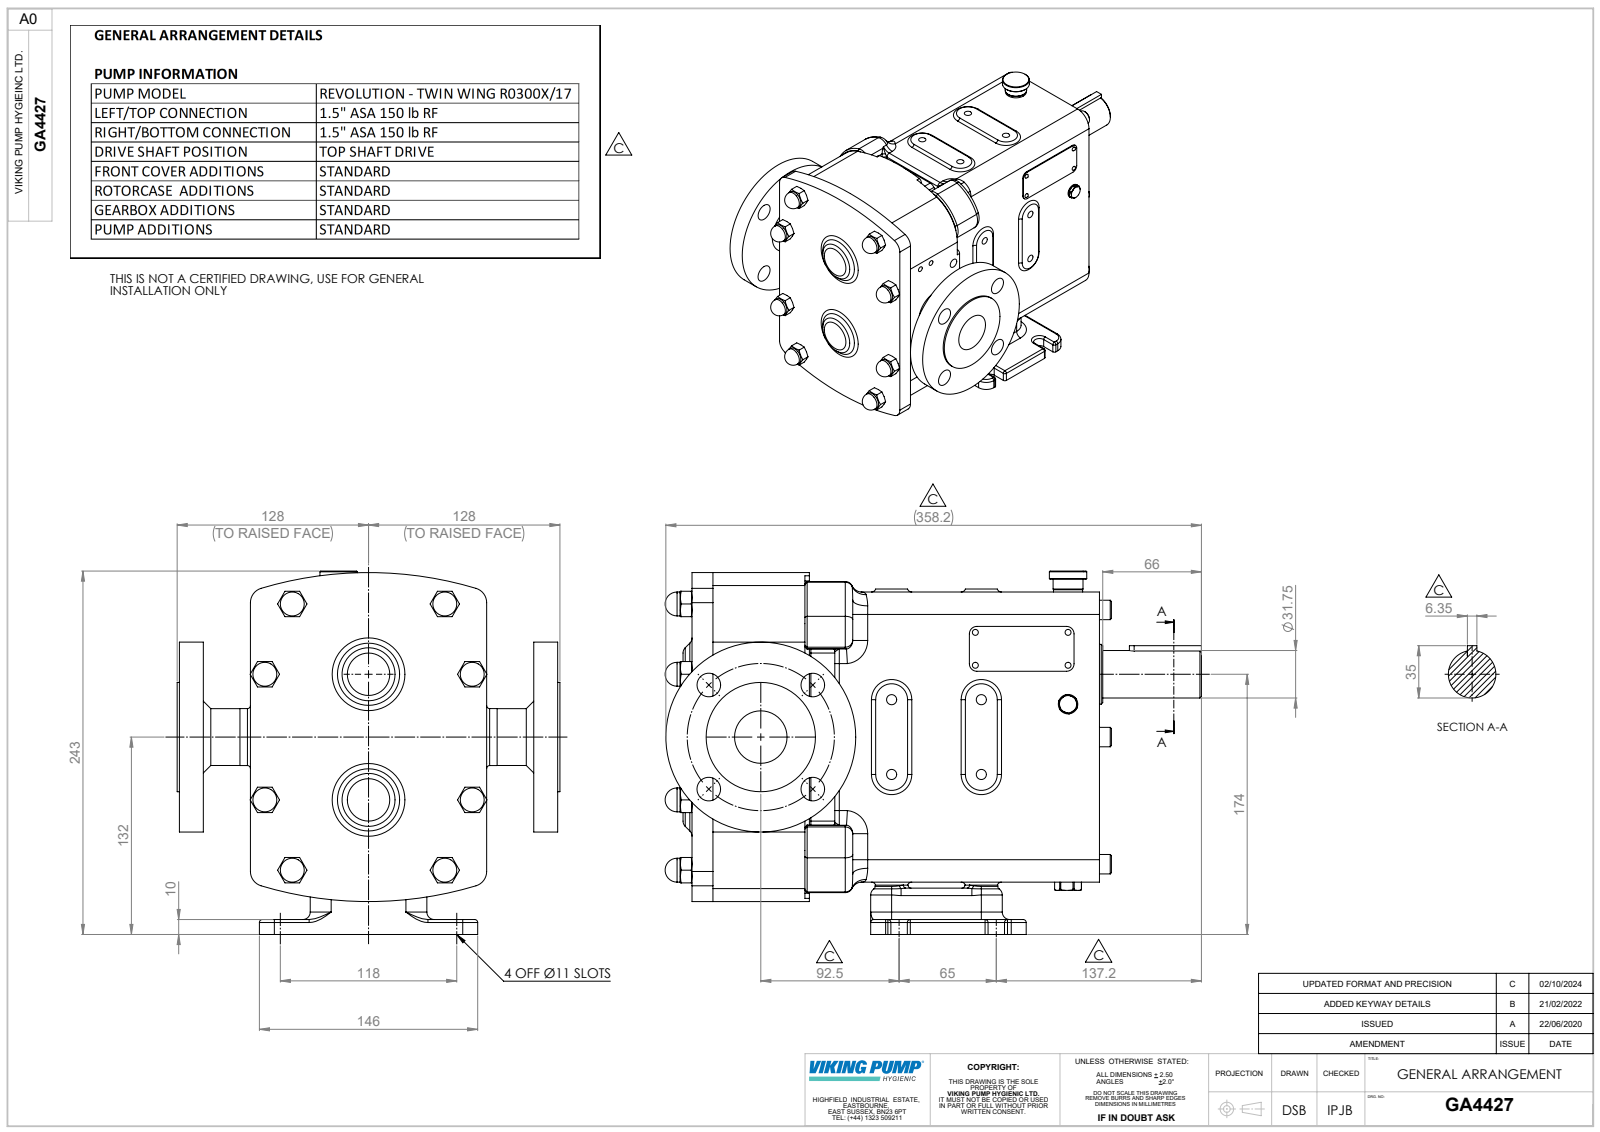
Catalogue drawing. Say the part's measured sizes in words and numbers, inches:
The part is named "Copy of Z94-5301-22 - 1.5 INCH ASA 150^GA4427; GA4427; Copy of R0300 CPP H TSD^GA4427". Its 3-D file was written by "SolidWorks 2023 (AUTOMOTIVE_DESIGN)". It is 3 solids with 975 faces: 306 planar, 326 cylindrical and 343 other. Overall it measures 14.122 by 10.079 by 9.567 inches. Its volume is 447.4 cubic inches and its surface area 670.2 square inches. Round holes: 8 of diameter 0.268, 7 of diameter 0.622, 4 of diameter 0.197, 2 of diameter 0.337, 1 of diameter 0.906, 1 of diameter 1.382. Round bosses or shafts: 8 of diameter 0.63, 7 of diameter 0.512, 2 of diameter 1.496, 1 of diameter 5, 1 of diameter 2.878, 1 of diameter 1.575, 1 of diameter 1.5, 1 of diameter 1.25. Partial cylindrical surfaces (rounded edges, fillets, slot ends): 30 of radius 0.394, 28 of radius 0.118, 24 of radius 0.079, 19 of radius 0.197, 8 of radius 0.232, 8 of radius 0.591, 4 of radius 0.217, 4 of radius 0.315. The main face-to-face distances are 7.638, 0.945, 4.331, 6.516, 2.185, 10.728, 1.24, 7.461, 5.276, 0.63. The hole center spacings are 1.937, 1.969, 2.362, 2.739, 3.075, 3.874, 0.494, 0.551.
